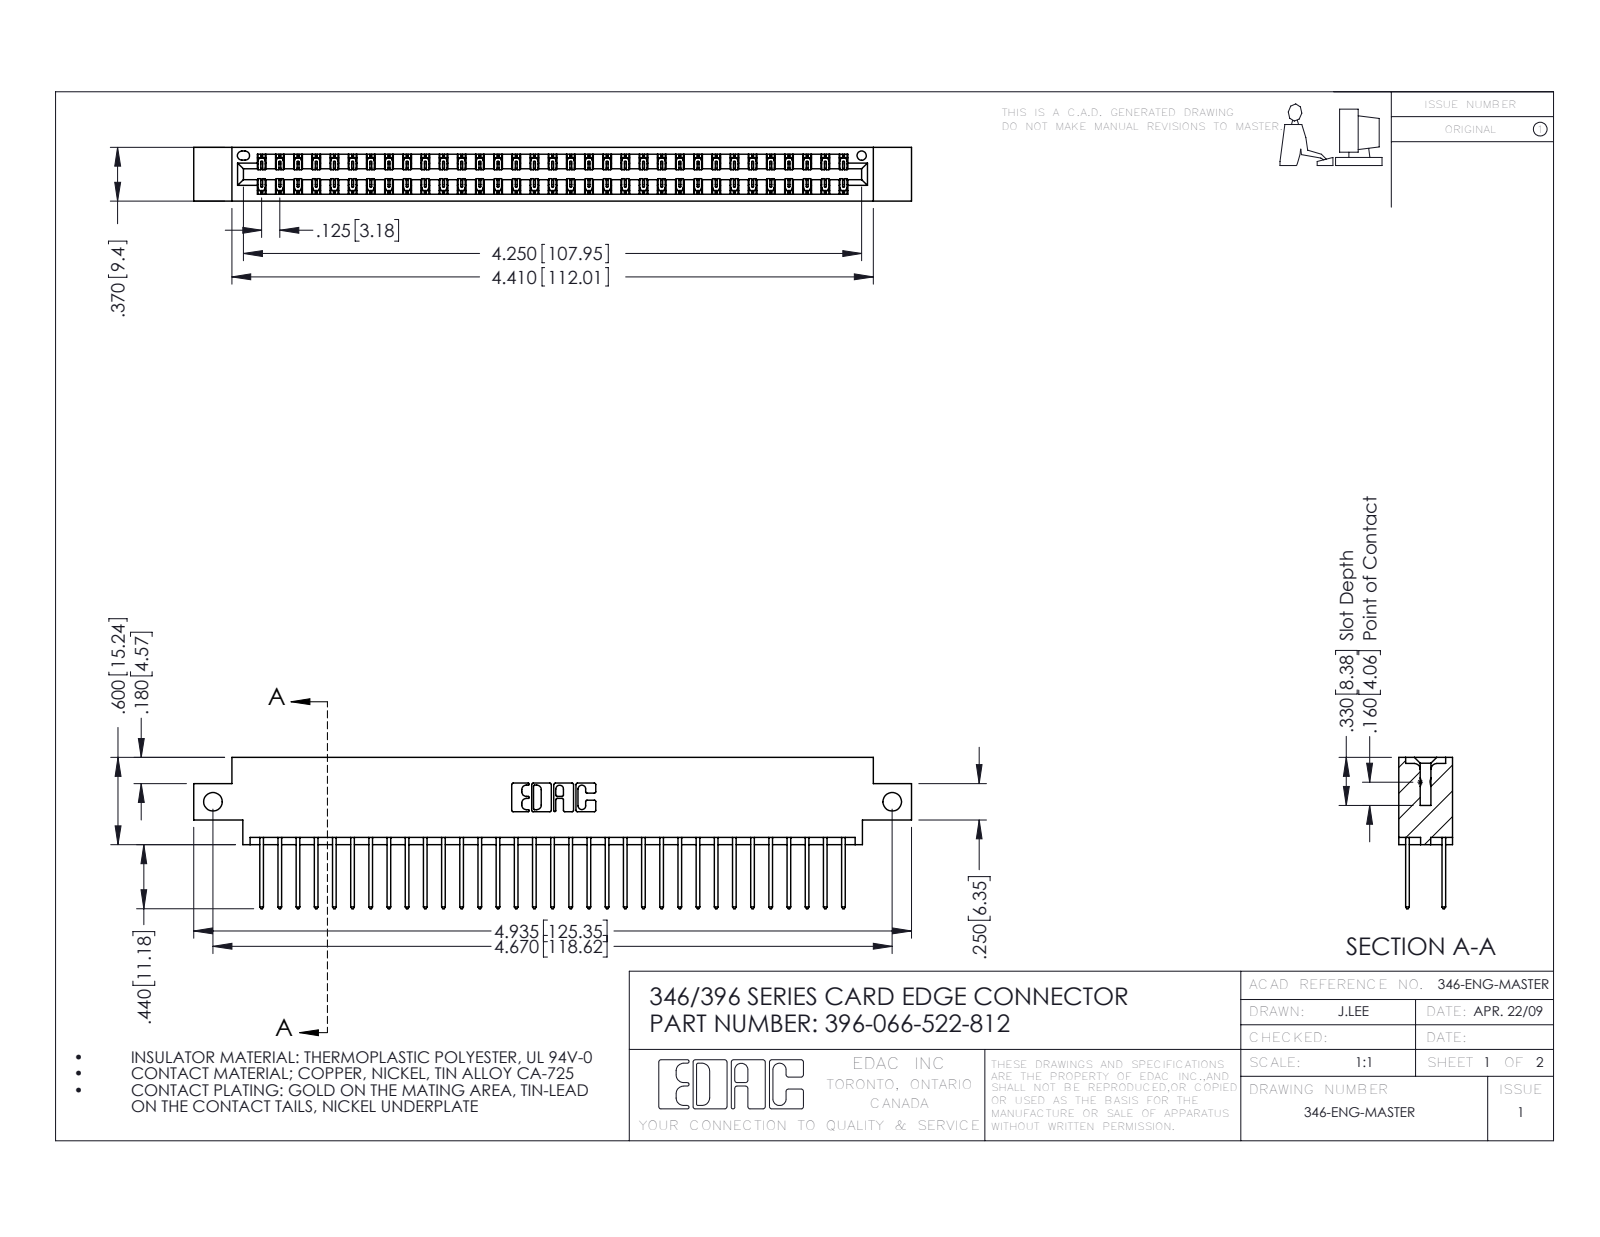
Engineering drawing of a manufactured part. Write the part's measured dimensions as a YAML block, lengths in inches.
part_name: "396-066-522-812; 345-292-001_345-293-122; 346 Part_0.170 Offset - Side Mount"
step_written_by: "SolidWorks 2016 (CONFIG_CONTROL_DESIGN)"
units: inches
bodies: {solids: 67, faces: 3558, planar: 2390, cylindrical: 1168, other: 0}
overall_size: [4.935, 1.04, 0.37]
volume: 0.737
surface_area: 26.8
round_holes:
  - {diameter: 0.128, count: 2}
  - {diameter: 0.064, count: 1}
partial_cylinders:
  - {radius: 0.006, count: 99}
  - {radius: 0.01, count: 66}
  - {radius: 0.01, count: 22}
  - {radius: 0.007, count: 6}
  - {radius: 0.031, count: 6}
  - {radius: 0.026, count: 3}
  - {radius: 0.014, count: 2}
  - {radius: 0.022, count: 2}
face_to_face_distances: [0.048, 0.322, 0.25, 0.37, 0.072, 0.298, 0.025, 0.275, 0.148, 0.222]
hole_center_spacings: [4.67]
